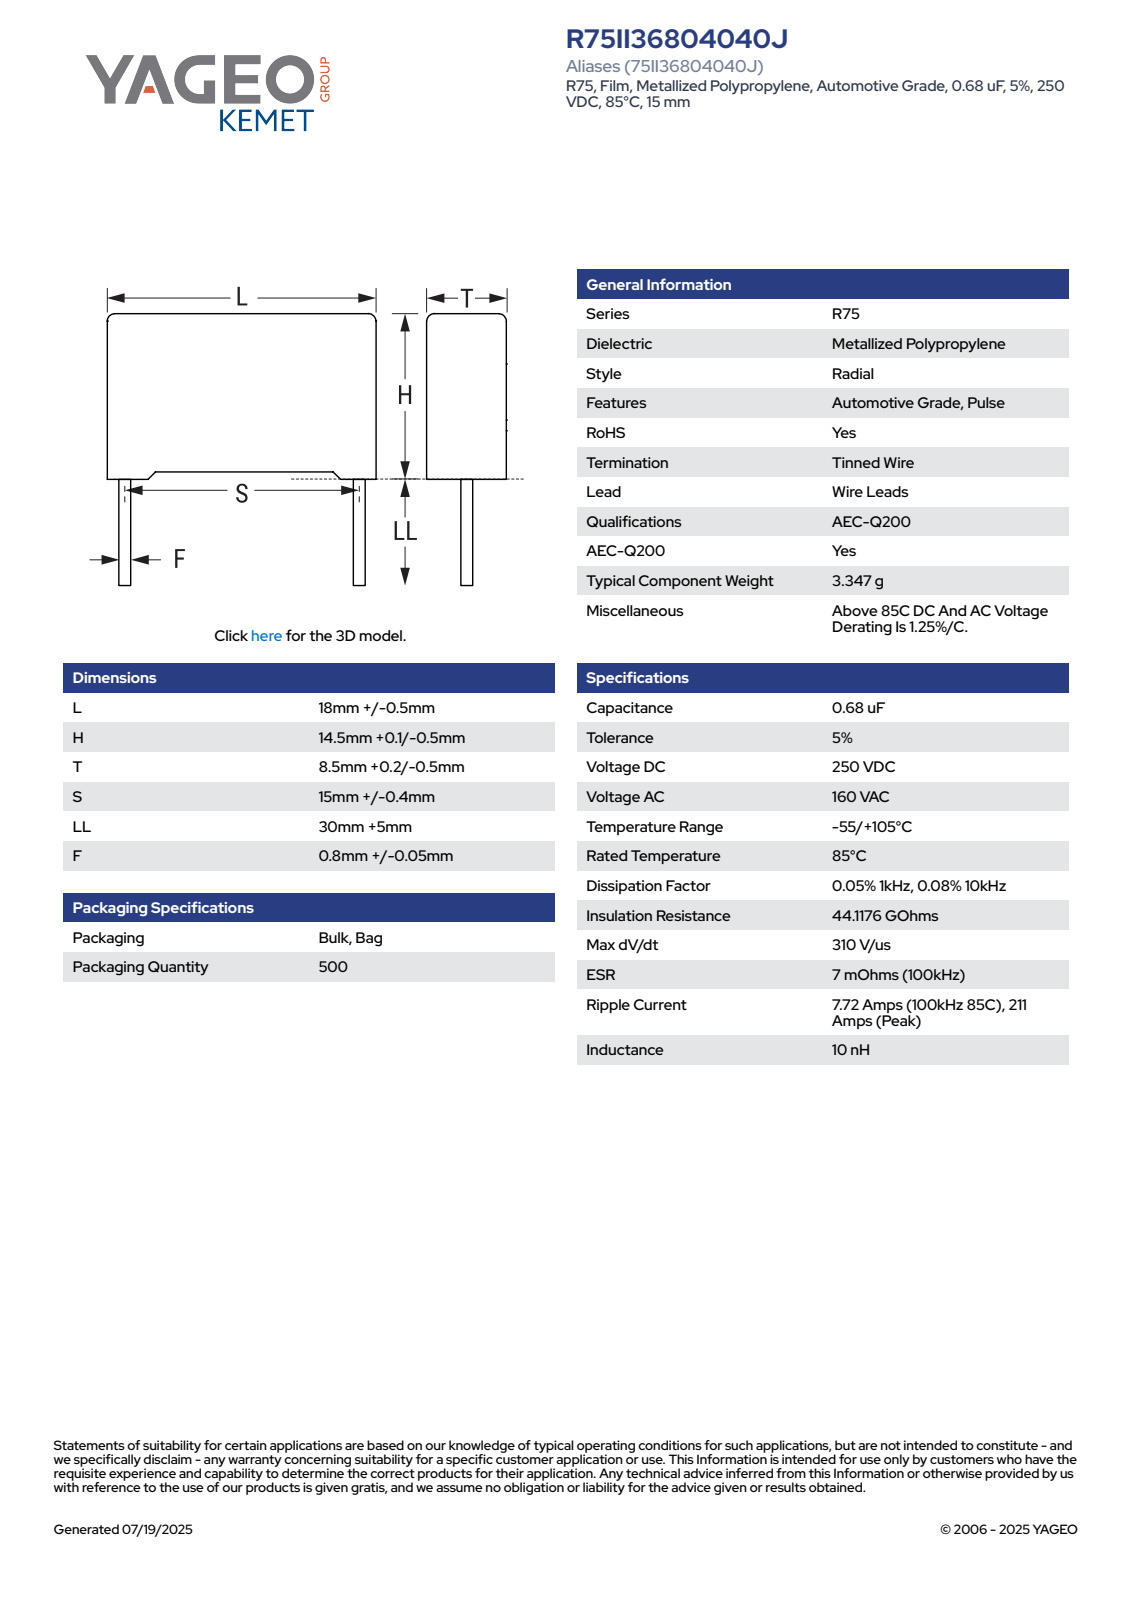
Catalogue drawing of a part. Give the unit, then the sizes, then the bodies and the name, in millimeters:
Units: millimetres
Overall size (bounding box): 49.6 × 18.5 × 8.71
Round bosses / shafts (diameter × count): ⌀0.85 ×2
Partial cylindrical surfaces — rounded edges, fillets, slot ends (radius × count): R0.5 ×4
Main face-to-face distances: 8.7, 13.85, 18.5, 0.62, 0.75, 14.6, 8.08, 0.5, 14.1, 17.88
Volume: 2 284 mm³ · Surface area: 1 336 mm²
Bodies: 4 solids, 85 faces (77 planar, 8 cylindrical, 0 other)
Part name (STEP PRODUCT): CFR_RB2_18X14.5X8.5_L18.5H14.6T8.7S15LL35F0.85
STEP written by: SolidWorks 2021 (AUTOMOTIVE_DESIGN)
